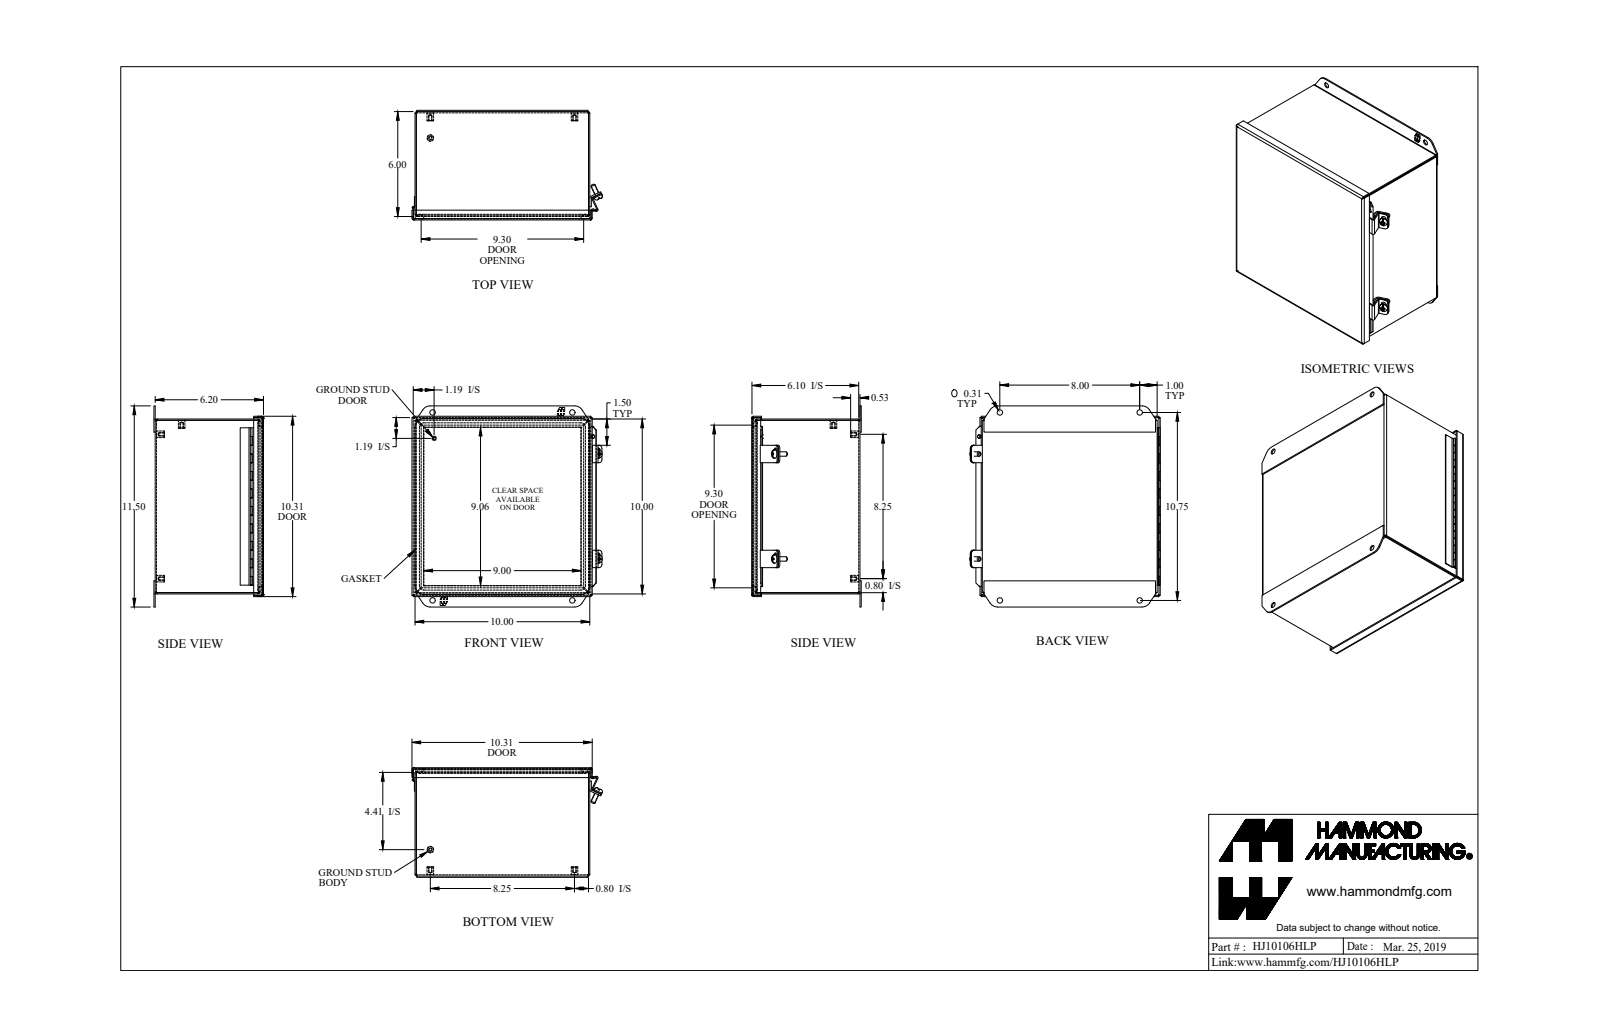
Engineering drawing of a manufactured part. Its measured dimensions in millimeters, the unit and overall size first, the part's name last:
Units: millimetres
Overall size (bounding box): 292.1 × 276.8 × 159.2
Round holes (diameter × count): ⌀4 ×5, ⌀8 ×4, ⌀5.4 ×2, ⌀1.3 ×1
Round bosses / shafts (diameter × count): ⌀9.5 ×5, ⌀6.4 ×3, ⌀12.2 ×2, ⌀4.8 ×1, ⌀2.5 ×1, ⌀1.1 ×1
Partial cylindrical surfaces — rounded edges, fillets, slot ends (radius × count): R6.4 ×16, R0.9 ×13, R2.7 ×13, R0.3 ×4, R3.6 ×4, R4.8 ×4, R12.7 ×4, R12.7 ×4
Main face-to-face distances: 1.8, 252.2, 155.6, 157.4, 254, 250.3, 153.7, 3.7, 159.2, 157.4
Hole centre spacings: 31.9, 208.8, 209.6, 241.3, 317.5, 203.2, 273.1, 296.3
Volume: 666 300 mm³ · Surface area: 736 800 mm²
Bodies: 20 solids, 745 faces (398 planar, 219 cylindrical, 128 other)
Part name (STEP PRODUCT): HJ10106HLP
STEP written by: SolidWorks 2018 (AUTOMOTIVE_DESIGN)
